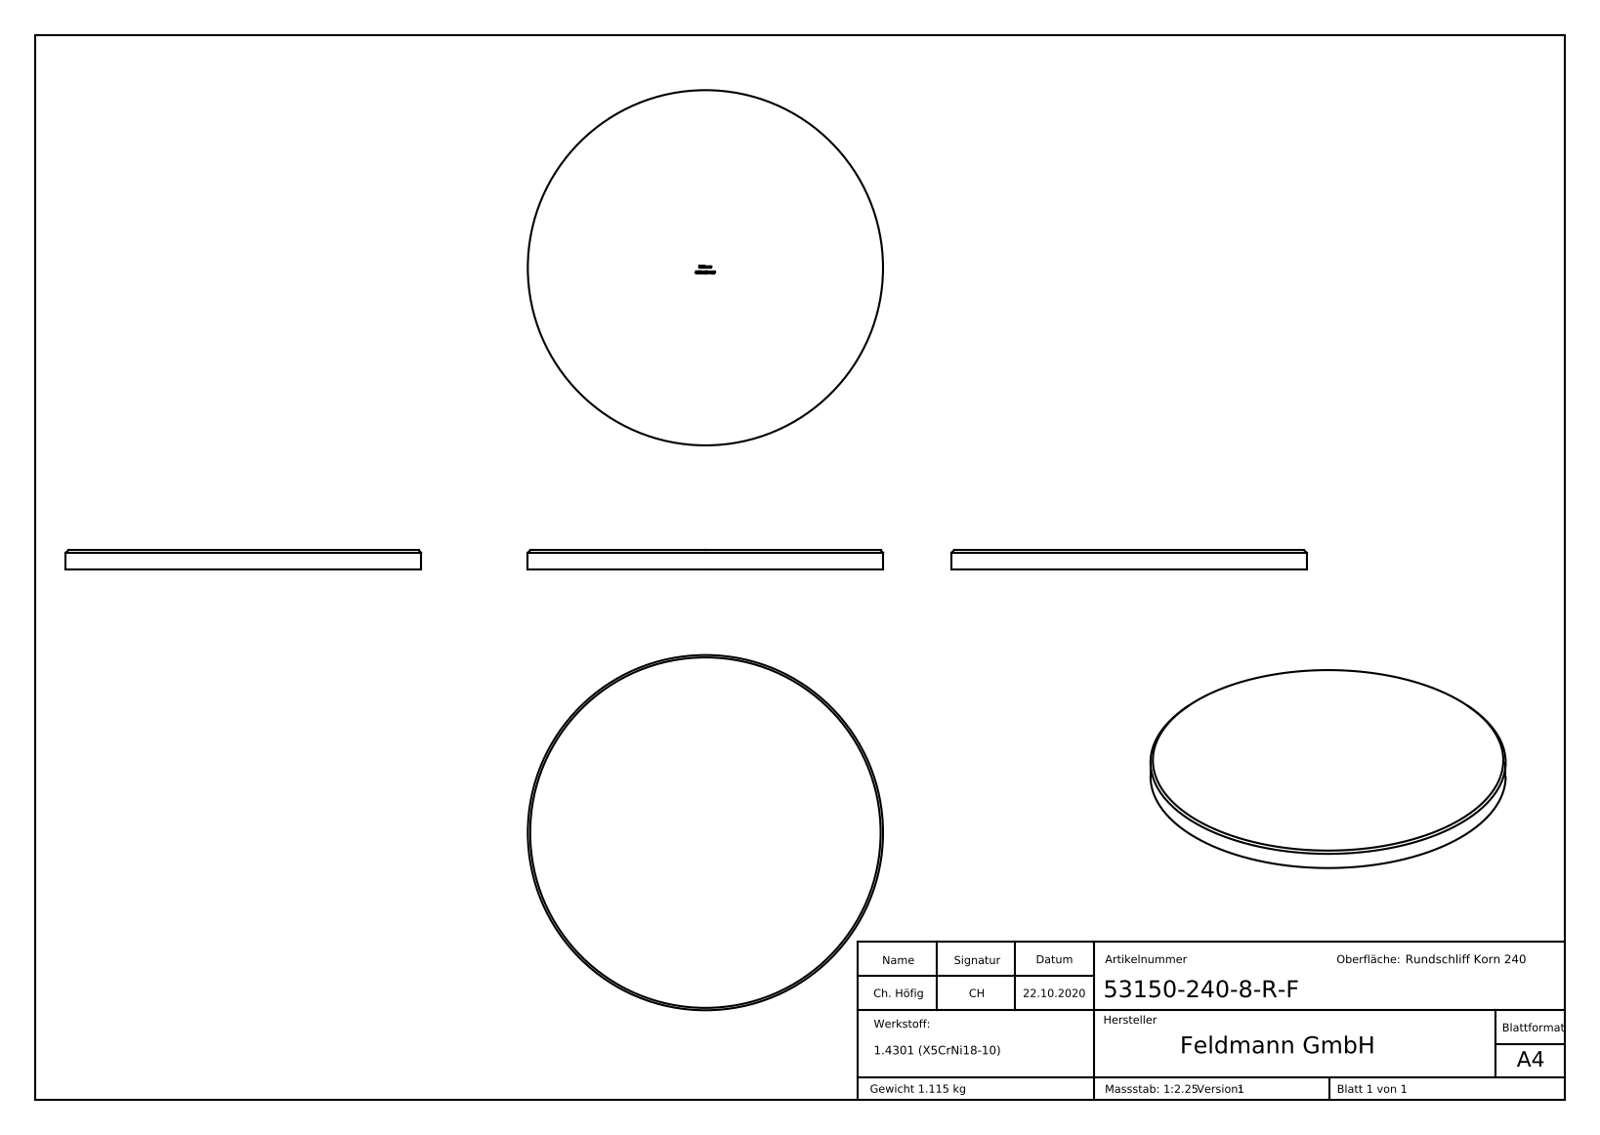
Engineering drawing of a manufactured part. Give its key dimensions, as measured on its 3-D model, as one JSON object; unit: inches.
{"part_name": "53150-240-8-R-F", "step_written_by": "SolidWorks 2018 (CONFIG_CONTROL_DESIGN)", "units": "inches", "bodies": {"solids": 1, "faces": 293, "planar": 165, "cylindrical": 2, "other": 126}, "overall_size": [5.906, 5.906, 0.315], "volume_in3": 8.613, "surface_area_in2": 60.21, "round_bosses_or_shafts": [[5.906, 1]], "face_to_face_distances": [0.315, 0.311, 0.018, 0.048, 0.157, 0.115, 0.068, 0.021, 0.092, 0.091]}
